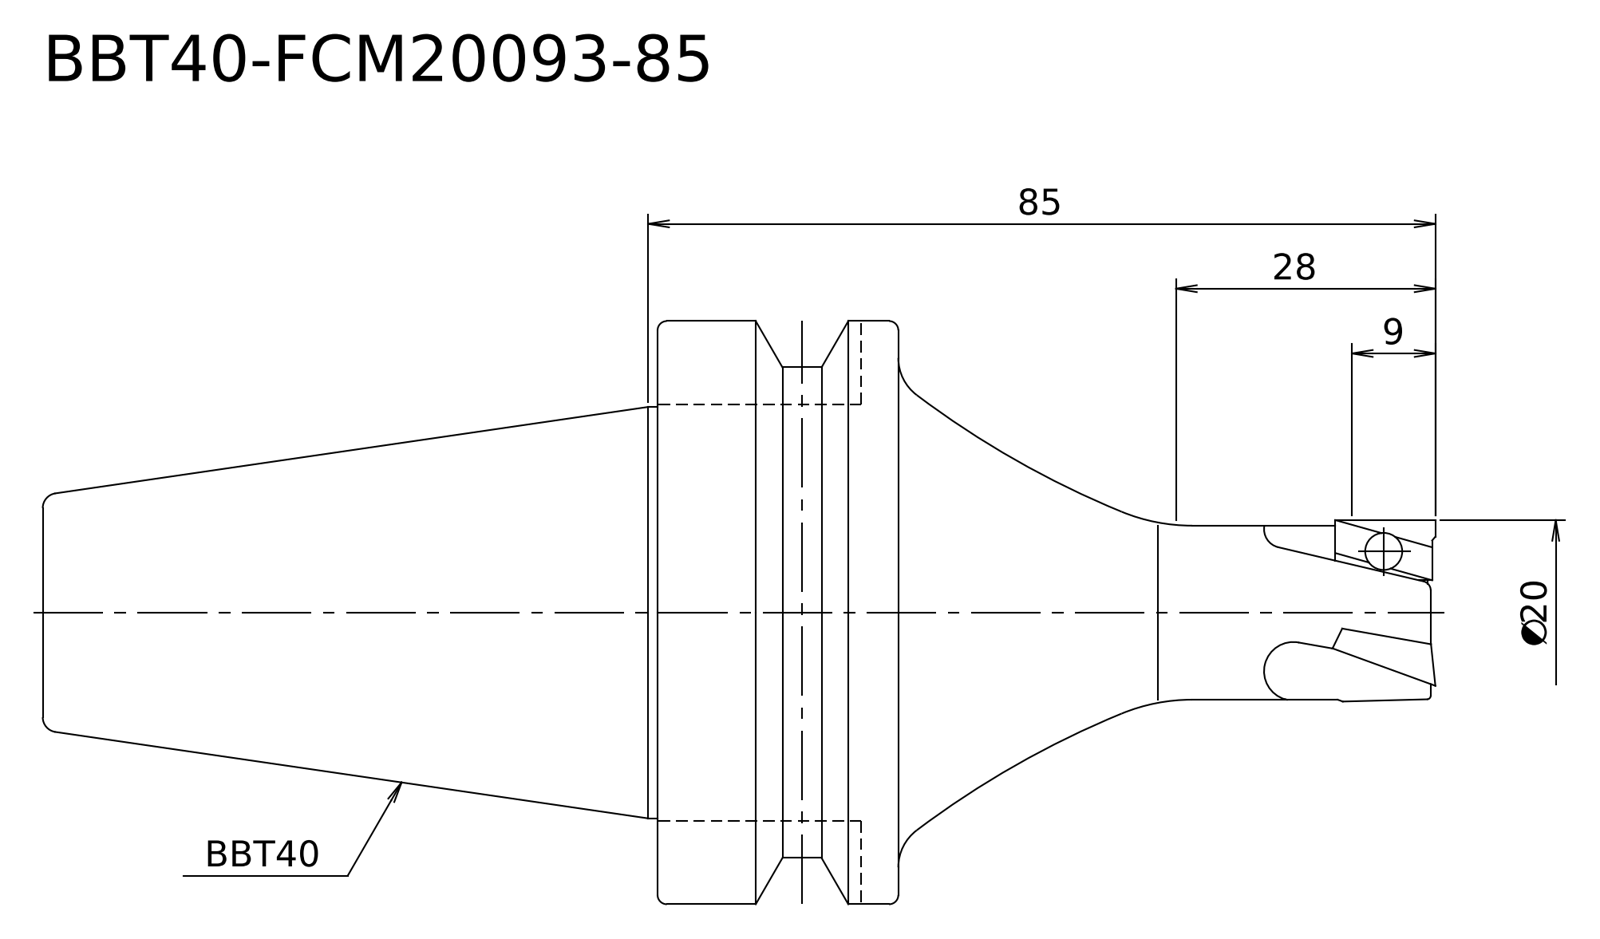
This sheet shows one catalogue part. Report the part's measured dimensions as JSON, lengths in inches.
{"step_written_by": "Kubotek KeyCreator V8.5.1 (14335) (CONFIG_CONTROL_DESIGN)", "units": "inches", "bodies": {"solids": 1, "faces": 17, "planar": 4, "cylindrical": 6, "other": 7}, "overall_size": [5.921, 2.48, 2.48], "volume_in3": 10.64, "surface_area_in2": 34.07, "round_bosses_or_shafts": [[2.48, 1], [2.087, 1], [1.75, 1], [0.787, 1], [0.74, 1]], "face_to_face_distances": [1.024, 3.638, 2.614, 2.283, 3.307, 5.921]}
